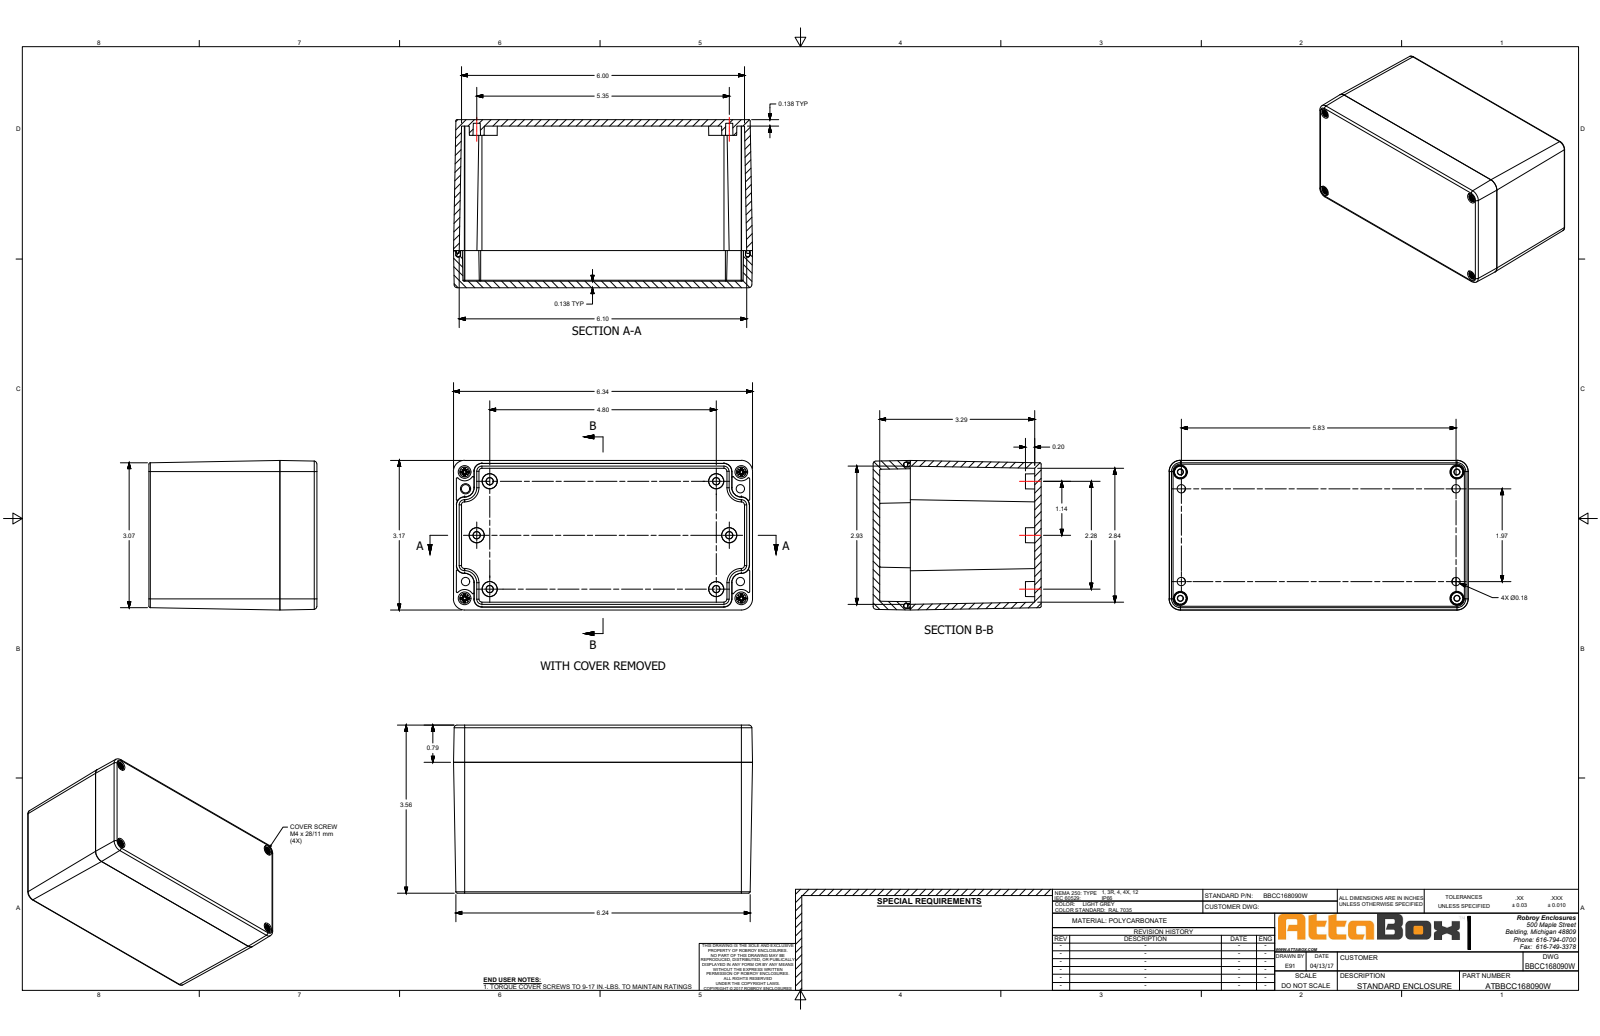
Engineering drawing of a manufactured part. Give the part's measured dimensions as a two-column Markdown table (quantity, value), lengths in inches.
| quantity | value |
| --- | --- |
| part name | BBCC168090W |
| STEP written by | SolidWorks 2018 (AUTOMOTIVE_DESIGN) |
| units | inches |
| bodies | 11 solids, 1640 faces (607 planar, 440 cylindrical, 593 other) |
| overall size | 6.339 × 3.564 × 3.169 |
| volume | 14.18 in³ |
| surface area | 252 in² |
| round holes (diameter × count) | 0.177 × 8, 0.128 × 4, 0.189 × 4, 0.201 × 4, 0.276 × 4, 0.291 × 4, 0.295 × 4 |
| round bosses / shafts (diameter × count) | 0.268 × 4, 0.173 × 4, 0.157 × 4, 0.13 × 4 |
| partial cylindrical surfaces (radius × count) | 0.039 × 48, 0.02 × 38, 0.079 × 8, 0.177 × 8, 0.197 × 8, 0.031 × 4, 0.059 × 4, 0.102 × 4 |
| main face-to-face distances | 0.138, 3.425, 0.12, 3.563, 3.287, 3.049, 3.169, 0.122, 0.175, 2.874 |
| hole center spacings | 0.355, 2.323, 5.857, 6.291, 1.969, 2.677, 5.827, 5.866 |
